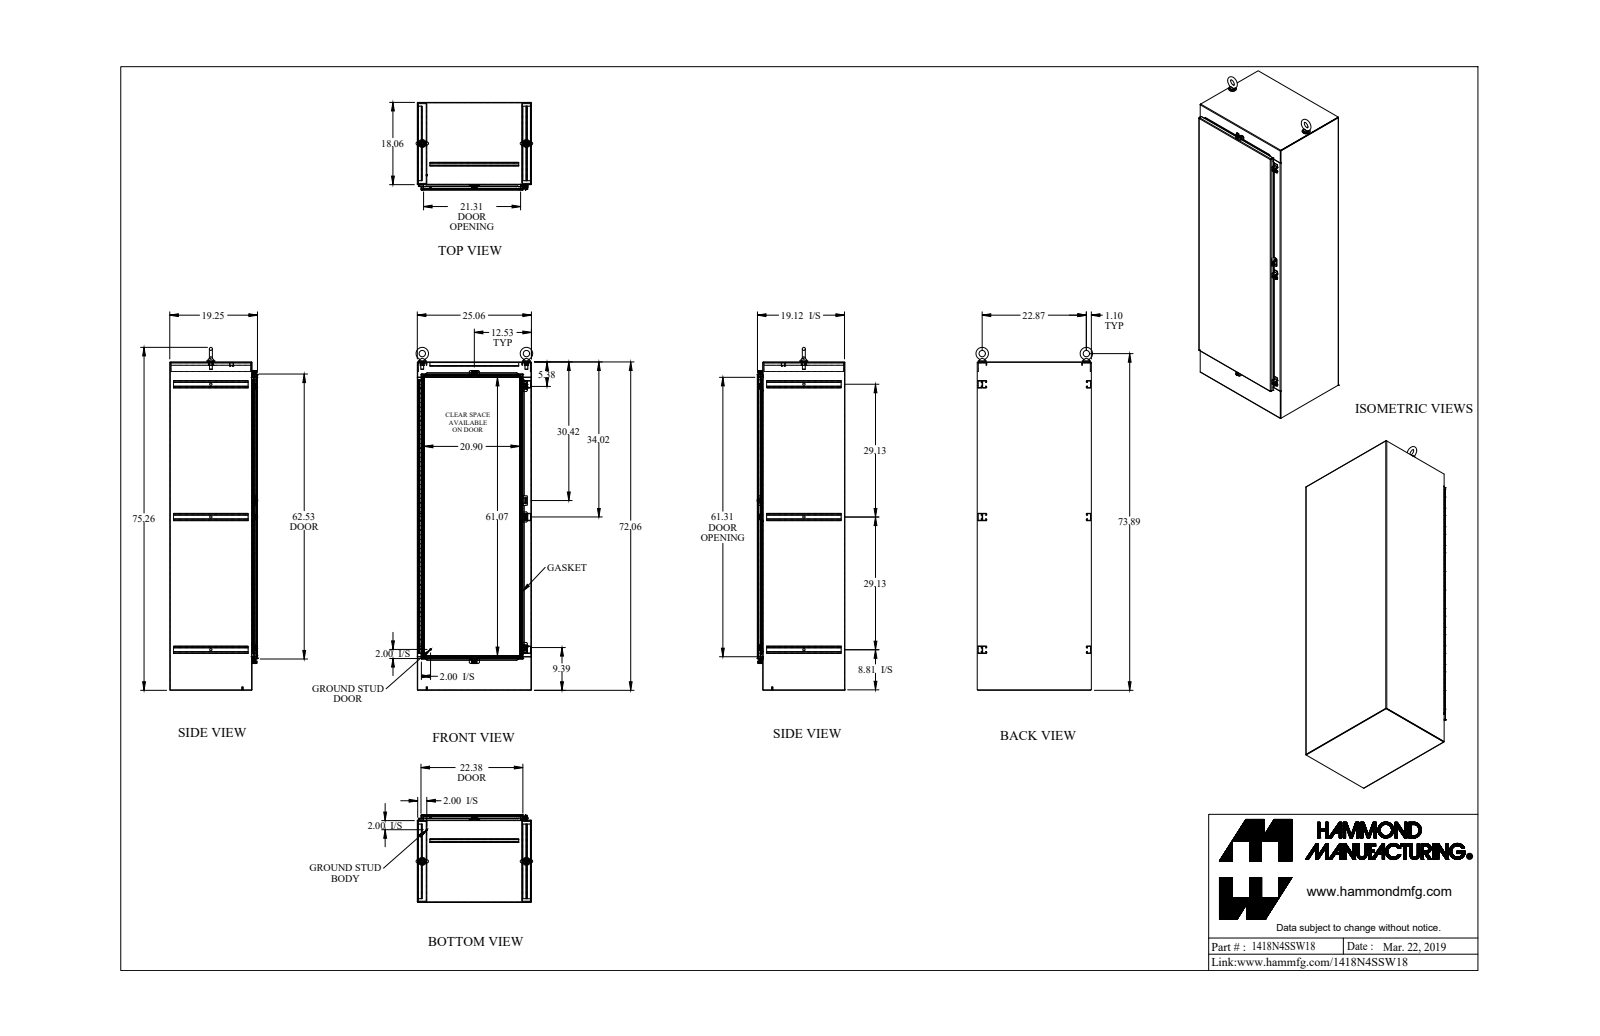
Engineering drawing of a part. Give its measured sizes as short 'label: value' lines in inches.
name: 1418N4SSW18
written by: SolidWorks 2019 (AUTOMOTIVE_DESIGN)
unit: in
bodies: 52 solids, 1734 faces (1076 planar, 574 cylindrical, 84 other)
size: 75.719 × 26.118 × 19.31
volume: 821.9 in³; area: 17 438 in²
holes: 10× ⌀0.304, 5× ⌀0.213, 5× ⌀0.265, 5× ⌀0.375, 3× ⌀0.5, 2× ⌀0.527, 2× ⌀0.625, 2× ⌀0.68, 2× ⌀0.75, 1× ⌀0.11, 1× ⌀0.125
bosses: 5× ⌀0.5, 5× ⌀0.39, 5× ⌀0.244, 2× ⌀1.75, 2× ⌀1.5, 2× ⌀1.25, 2× ⌀0.738, 2× ⌀0.313
rounds: 60× R0.043, 54× R0.138, 39× R0.048, 39× R0.143, 26× R0.25, 10× R0.06, 10× R0.141, 8× R0.125
face distances: 0.095, 19.152, 24.965, 24.87, 19.057, 19.247, 25.06, 1.187, 17.965, 71.965
hole spacings: 6, 12, 18, 24, 30, 36, 42, 29.13
